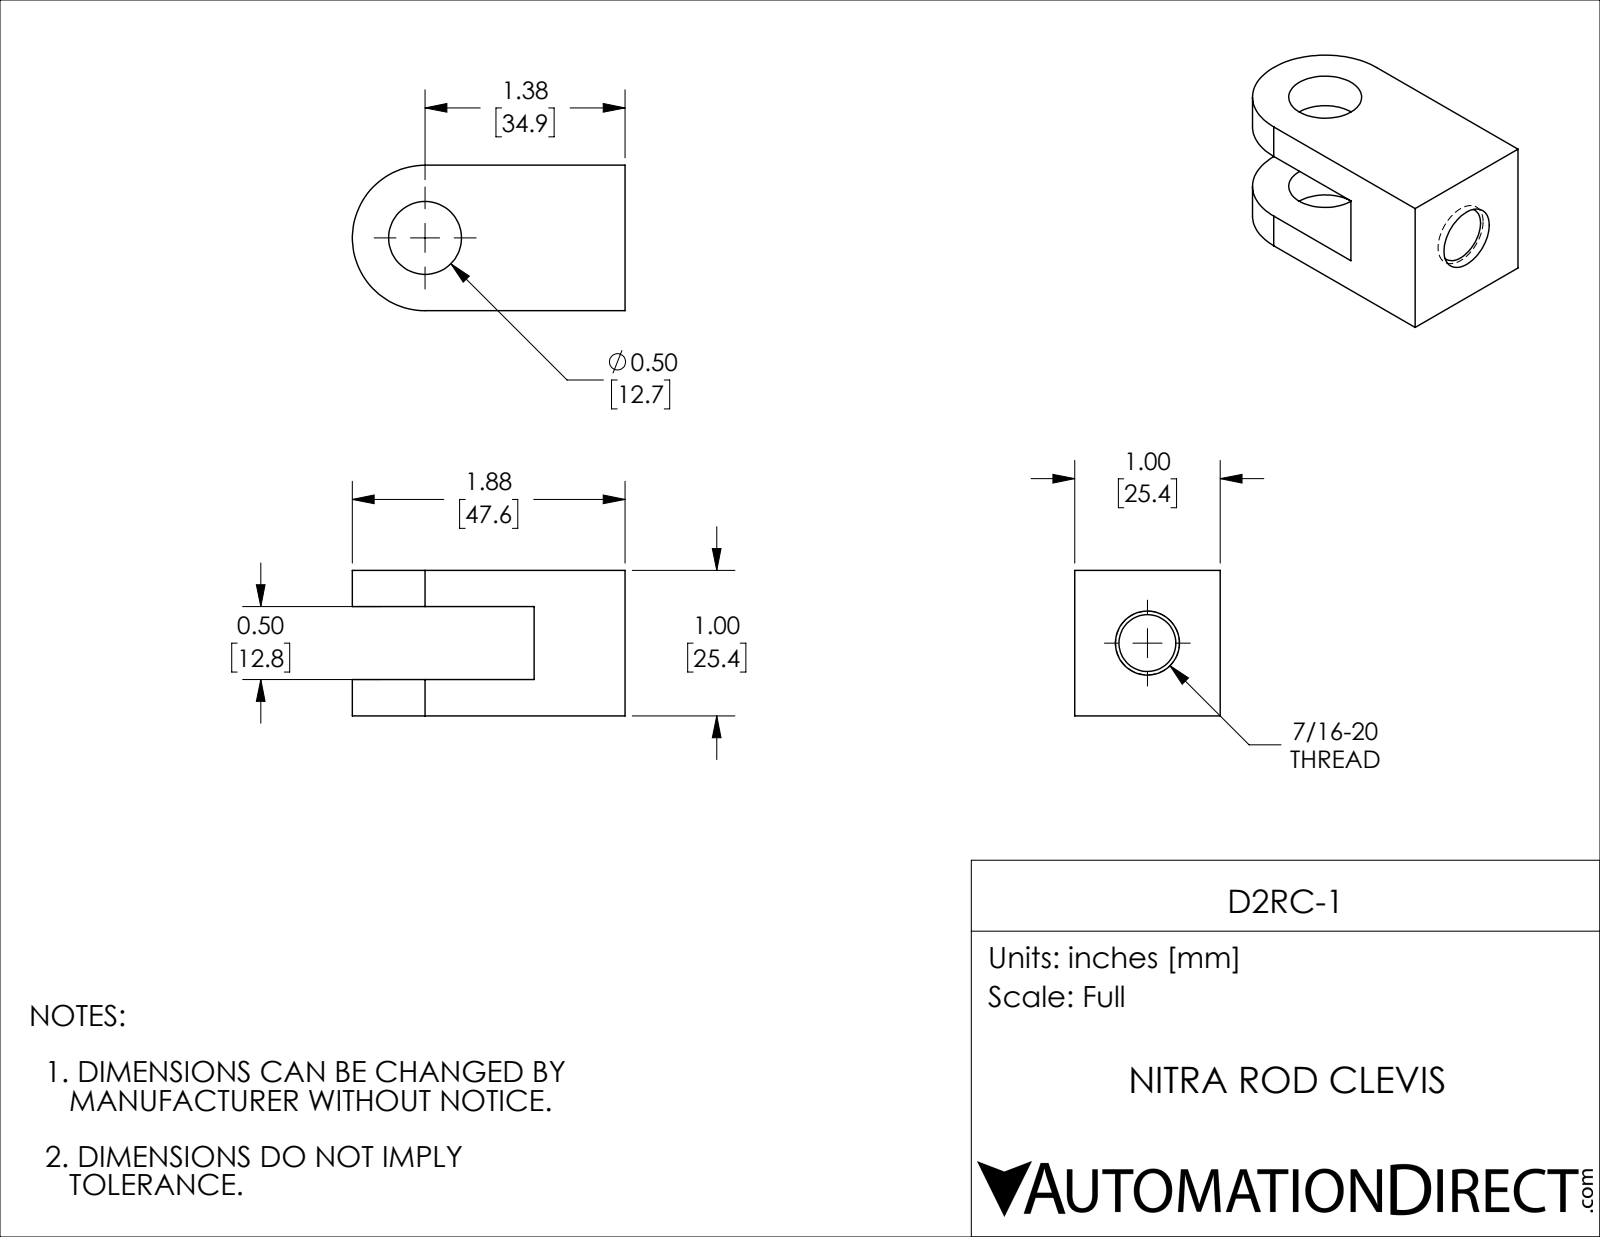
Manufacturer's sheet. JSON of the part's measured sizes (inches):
{"part_name": "D2RC-1", "step_written_by": "SolidWorks 2019 (CONFIG_CONTROL_DESIGN)", "units": "inches", "bodies": {"solids": 1, "faces": 20, "planar": 8, "cylindrical": 8, "other": 4}, "overall_size": [1.875, 1, 1], "volume_in3": 1.019, "surface_area_in2": 10.58, "round_holes": [[0.391, 1], [0.501, 1]], "partial_cylinders_radius": [[0.5, 1]], "face_to_face_distances": [1, 0.249, 0.751, 0.502, 0.625]}
